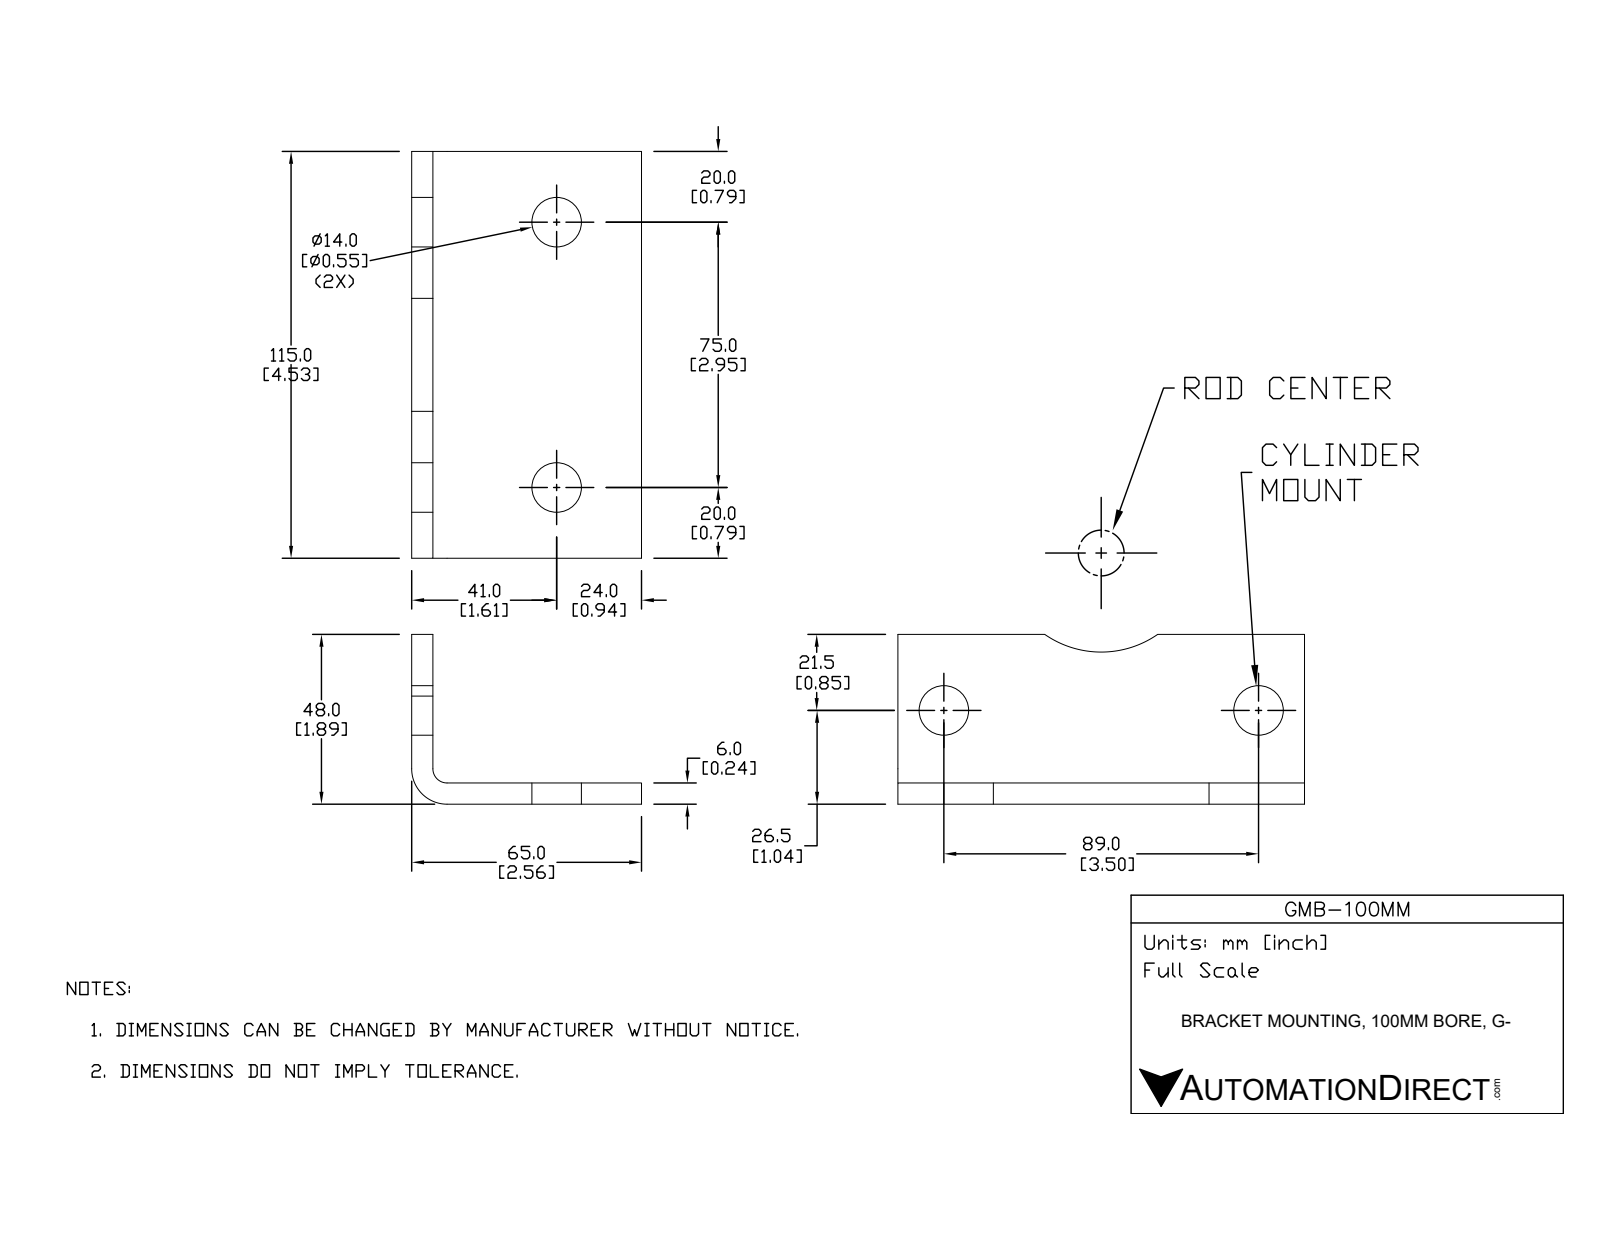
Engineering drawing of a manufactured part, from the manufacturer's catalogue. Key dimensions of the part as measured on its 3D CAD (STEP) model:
Part name (STEP PRODUCT): GMB-100MM
STEP written by: SolidWorks 2017 (AUTOMOTIVE_DESIGN)
Units: millimetres
Bodies: 1 solid, 24 faces (13 planar, 11 cylindrical, 0 other)
Overall size (bounding box): 115 × 65 × 48
Volume: 67 115 mm³ · Surface area: 26 062 mm²
Round holes (diameter × count): ⌀14 ×4
Partial cylindrical surfaces — rounded edges, fillets, slot ends (radius × count): R5 ×1, R11 ×1, R28 ×1
Main face-to-face distances: 6, 65, 59, 115, 48, 42
Hole centre spacings: 75, 89
